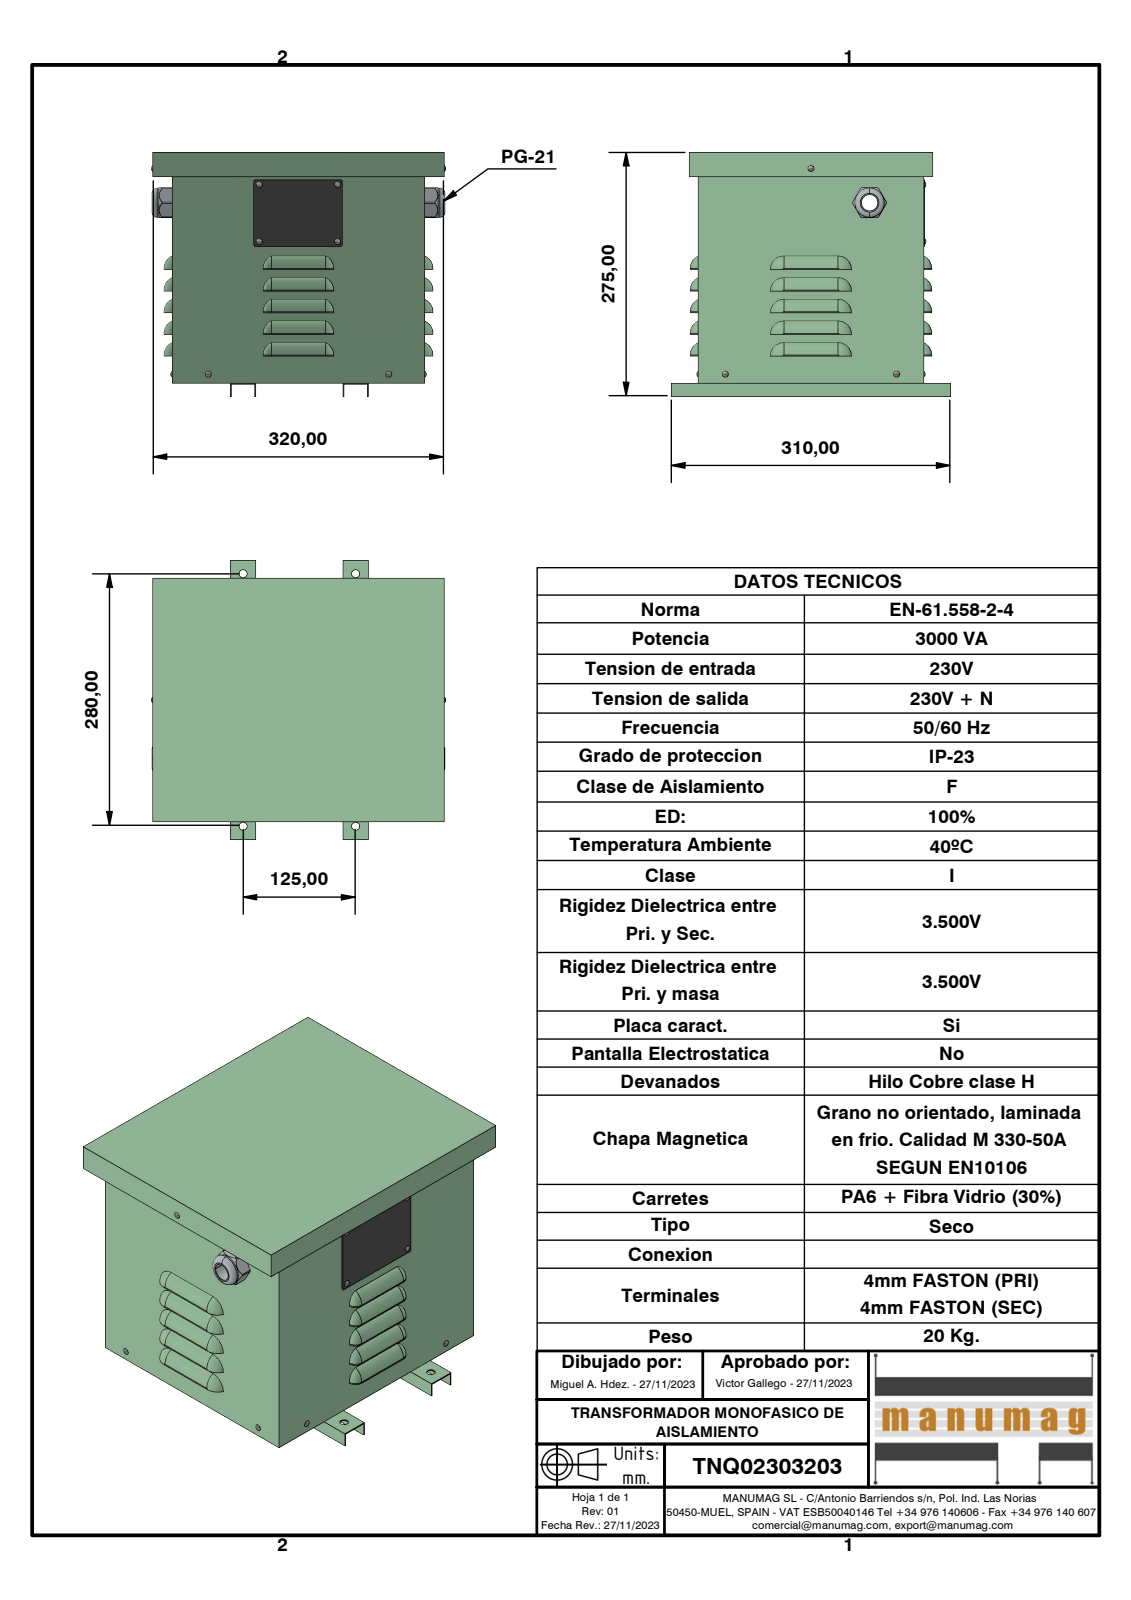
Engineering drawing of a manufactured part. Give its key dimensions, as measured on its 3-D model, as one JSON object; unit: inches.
{"part_name": "TNQ02303203; RC65 BASE; Rc65 PATA; RC65 CUERPO (+4 more)", "step_written_by": "Autodesk Inventor 2023 (AUTOMOTIVE_DESIGN)", "units": "inches", "bodies": {"solids": 22, "faces": 1711, "planar": 807, "cylindrical": 774, "other": 130}, "overall_size": [12.845, 12.205, 10.669], "volume_in3": 41.56, "surface_area_in2": 1677, "round_holes": [[0.157, 9], [0.354, 8], [0.079, 4], [0.709, 1], [1.181, 1]], "round_bosses_or_shafts": [[0.126, 9], [1.276, 1], [1.122, 1], [1.114, 1]], "partial_cylinders_radius": [[0.039, 398], [0.276, 20], [0.591, 20], [0.315, 10], [0.551, 10], [0.197, 8], [0.079, 4], [0.354, 4]], "face_to_face_distances": [0.039, 9.803, 10.039, 10.984, 9.843, 10.079, 9.764, 10, 10.945, 11.024], "hole_center_spacings": [2.559, 4.906, 5.533, 8.465, 9.783, 0.039, 2.48, 3.425]}
